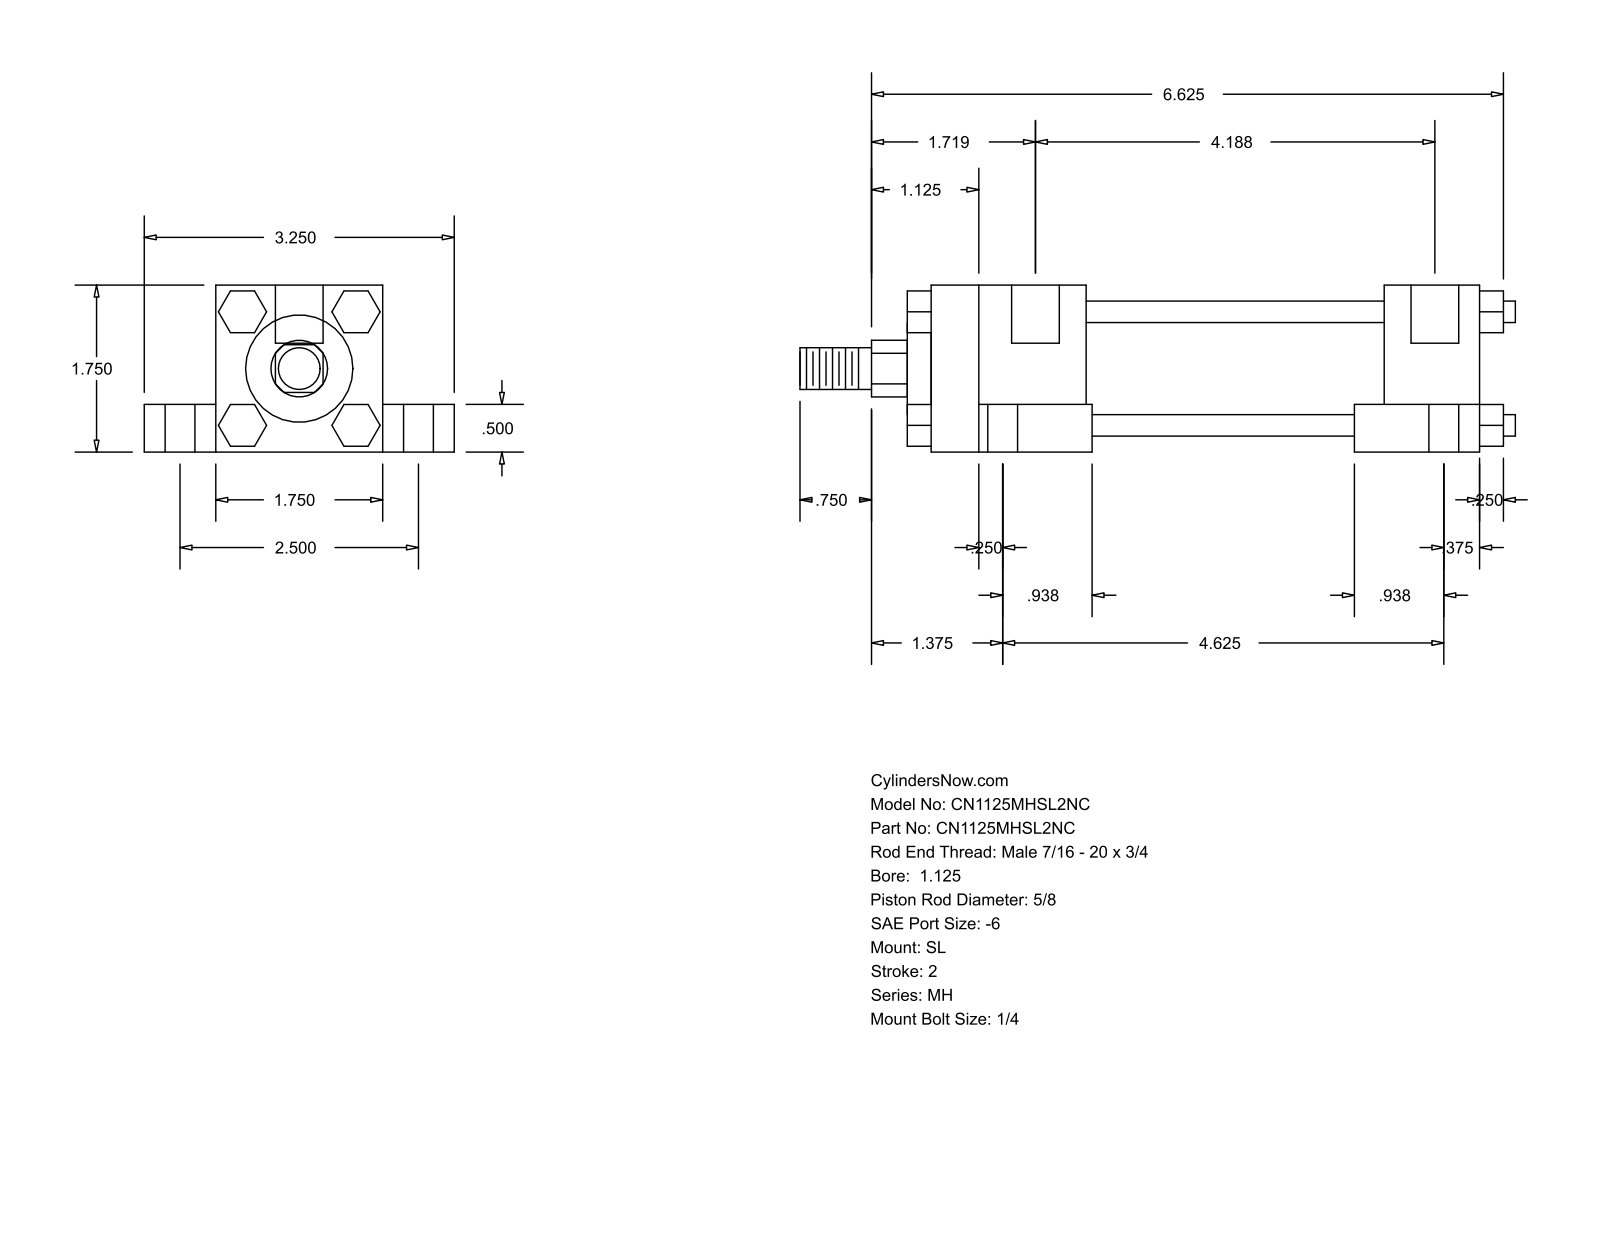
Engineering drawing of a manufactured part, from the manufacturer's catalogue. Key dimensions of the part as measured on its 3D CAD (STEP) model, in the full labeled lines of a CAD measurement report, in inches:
Part name (STEP PRODUCT): MH_SL__0112_0.625
STEP written by: GSSL Pune (CONFIG_CONTROL_DESIGN)
Units: inches
Bodies: 0 solids, 150 faces (114 planar, 36 cylindrical, 0 other)
Overall size (bounding box): 7.5 × 3.25 × 1.75
Round holes (diameter × count): ⌀0.219 ×4, ⌀0.313 ×4, ⌀0.563 ×4, ⌀0.5 ×2
Round bosses / shafts (diameter × count): ⌀0.225 ×4, ⌀1.375 ×1, ⌀1.125 ×1, ⌀0.625 ×1, ⌀0.437 ×1
Partial cylindrical surfaces — rounded edges, fillets, slot ends (radius × count): R0.297 ×1
Main face-to-face distances: 1.75, 0.75, 0.5, 1.25, 2.5, 0.25, 6, 0.437, 1.875, 1.313
Hole centre spacings: 1.254, 1.269, 1.296, 2.5, 4.063, 4.34, 4.46, 4.5
